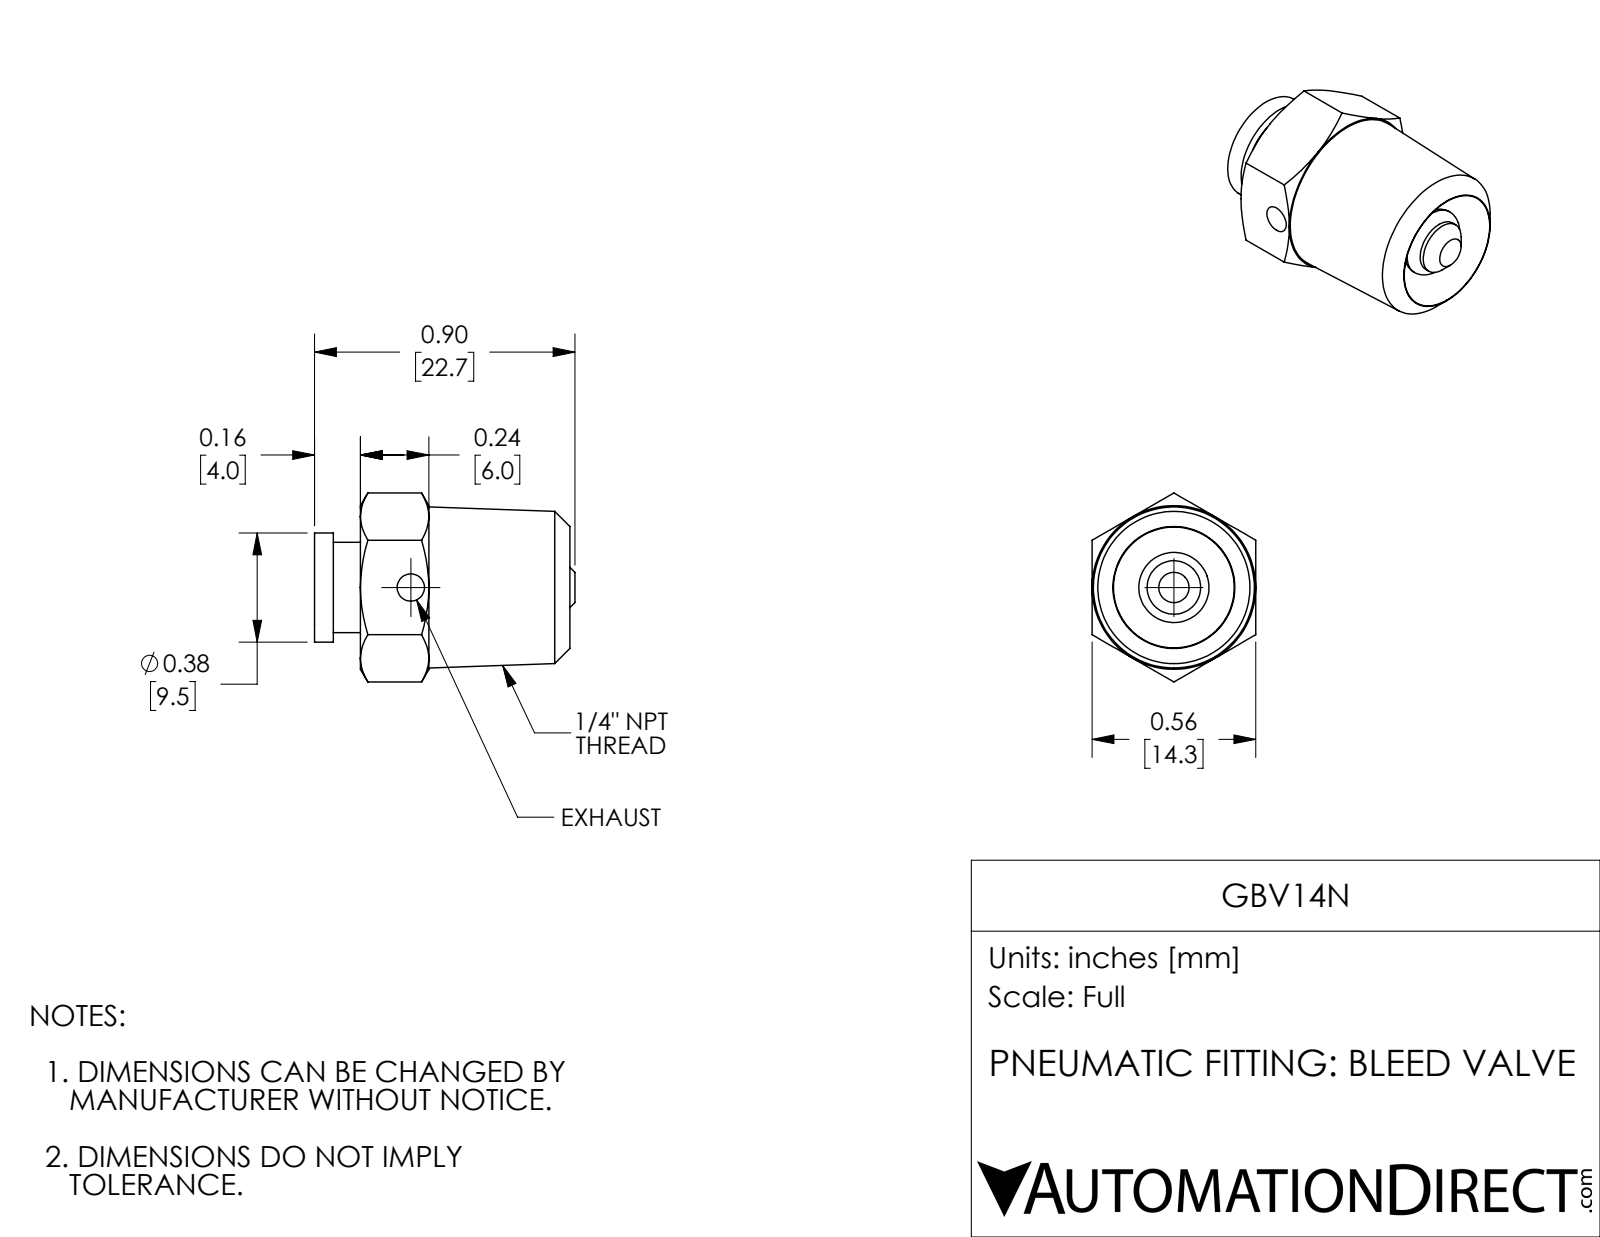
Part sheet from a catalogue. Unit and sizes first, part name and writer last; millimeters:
Units: millimetres
Overall size (bounding box): 22.7 × 16.5 × 14.3
Round holes (diameter × count): ⌀2.4 ×1, ⌀8.1 ×1
Round bosses / shafts (diameter × count): ⌀9.5 ×1, ⌀7.9 ×1, ⌀4.7 ×1
Main face-to-face distances: 14.3, 4, 9.6, 5.6, 4.7, 0.7, 4.9, 1.7, 2.4, 3
Volume: 2 690 mm³ · Surface area: 1 683 mm²
Bodies: 4 solids, 52 faces (16 planar, 10 cylindrical, 26 other)
Part name (STEP PRODUCT): GBV14N
STEP written by: SolidWorks 2018 (AUTOMOTIVE_DESIGN)
